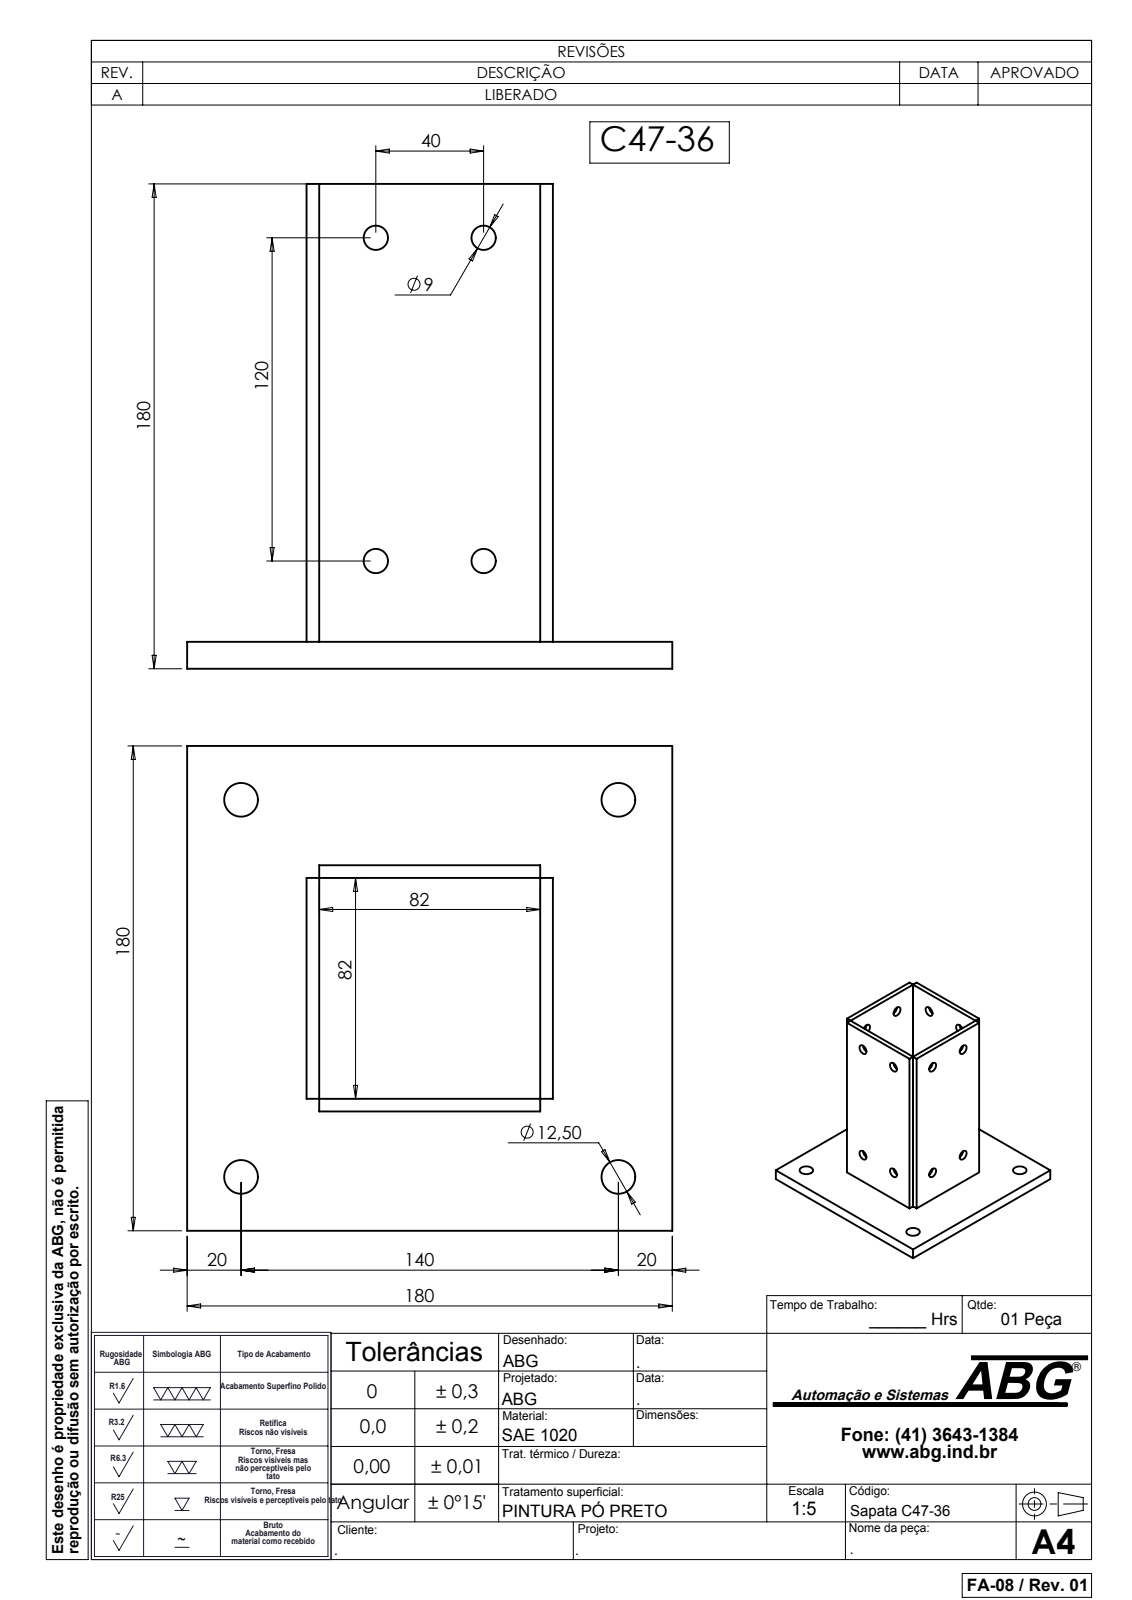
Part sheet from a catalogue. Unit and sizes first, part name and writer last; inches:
Units: inches
Overall size (bounding box): 7.087 × 7.087 × 7.087
Round holes (diameter × count): ⌀0.354 ×8, ⌀0.492 ×4
Main face-to-face distances: 0.185, 3.413, 0.394, 3.228, 3.598, 1.744, 1.929, 5.157, 5.343, 7.087
Hole centre spacings: 1.575, 4.724, 4.98, 5.512, 7.795
Volume: 35.17 in³ · Surface area: 300.2 in²
Bodies: 5 solids, 70 faces (30 planar, 40 cylindrical, 0 other)
Part name (STEP PRODUCT): C47-36; Lateral C47-36
STEP written by: SolidWorks 2007 (CONFIG_CONTROL_DESIGN)
